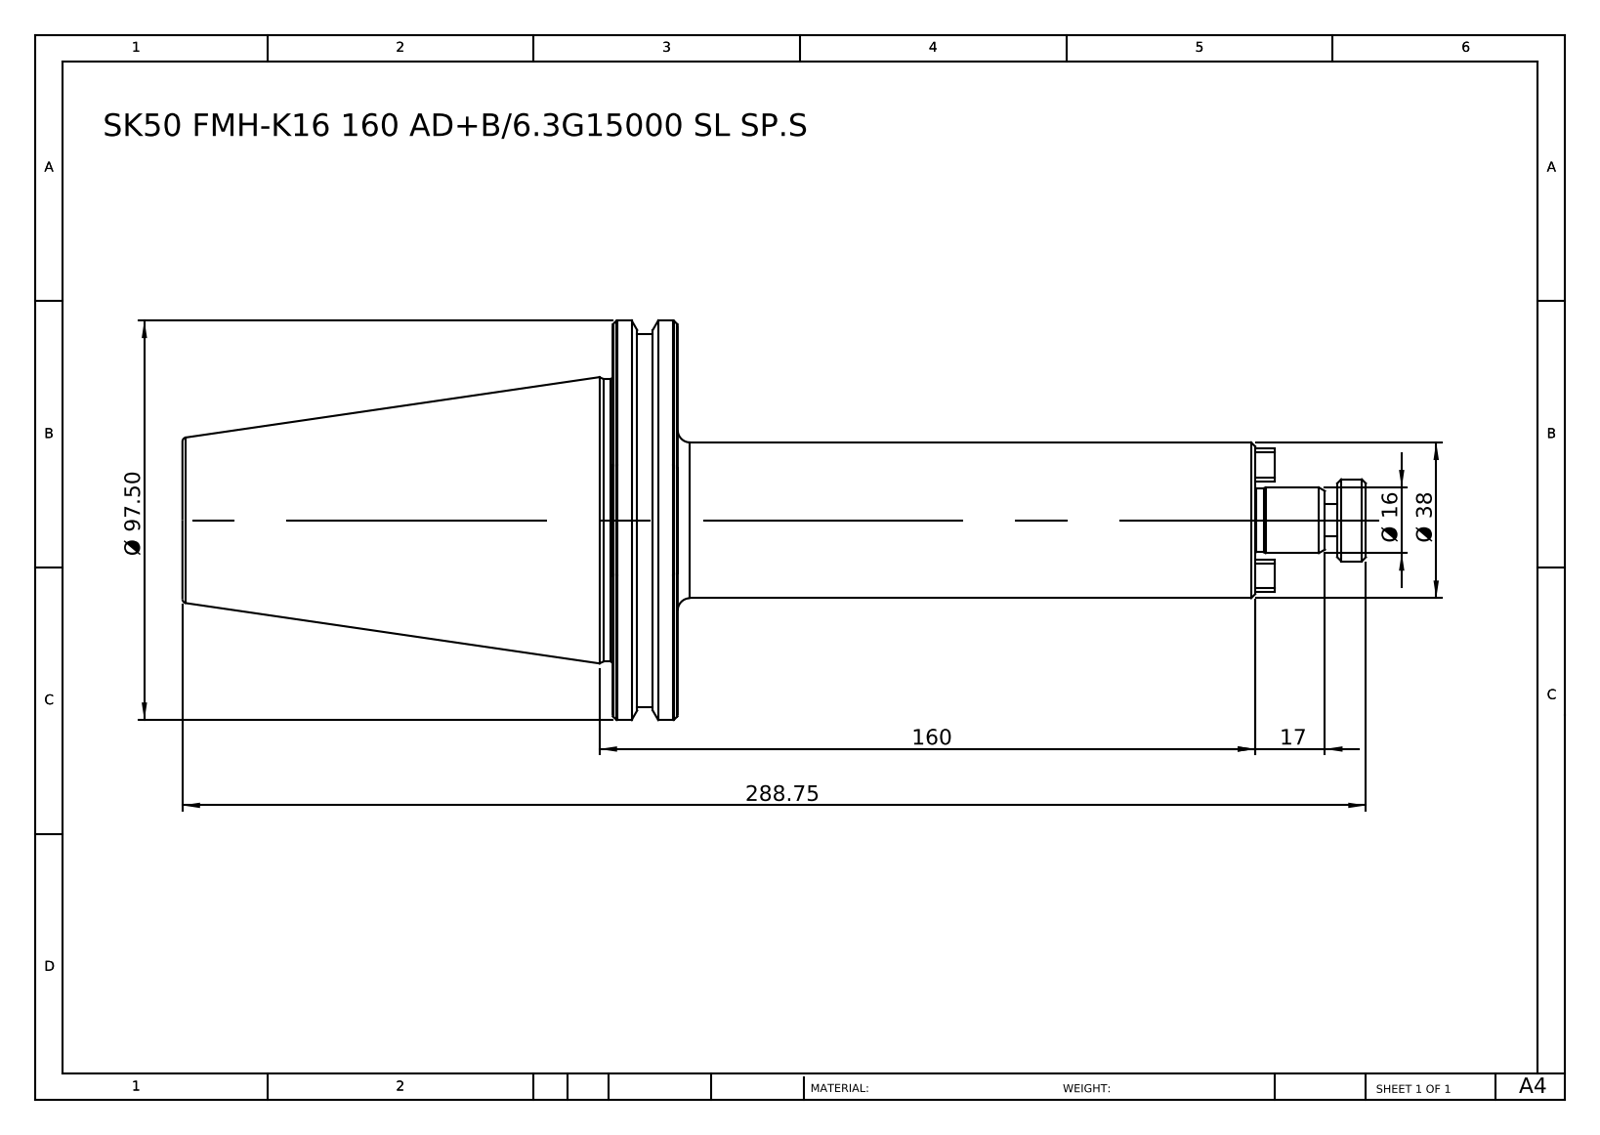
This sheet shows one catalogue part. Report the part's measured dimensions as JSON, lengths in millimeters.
{"part_name": "SK50 FMH-K16 160 AD+B-6.3G15000 SL SP", "step_written_by": "SolidWorks 2014 (CONFIG_CONTROL_DESIGN)", "units": "millimeters", "bodies": {"solids": 1, "faces": 105, "planar": 27, "cylindrical": 18, "other": 60}, "overall_size": [288.75, 97.5, 97.5], "volume_mm3": 539782, "surface_area_mm2": 55264, "round_bosses_or_shafts": [[97.5, 1], [91, 1], [69, 1], [38, 1], [20, 1], [16, 1], [15.6, 1], [8, 1]], "face_to_face_distances": [15.9, 120.85, 104.95, 140.9, 156.8, 261.75, 27, 147, 6.1, 9.8]}
